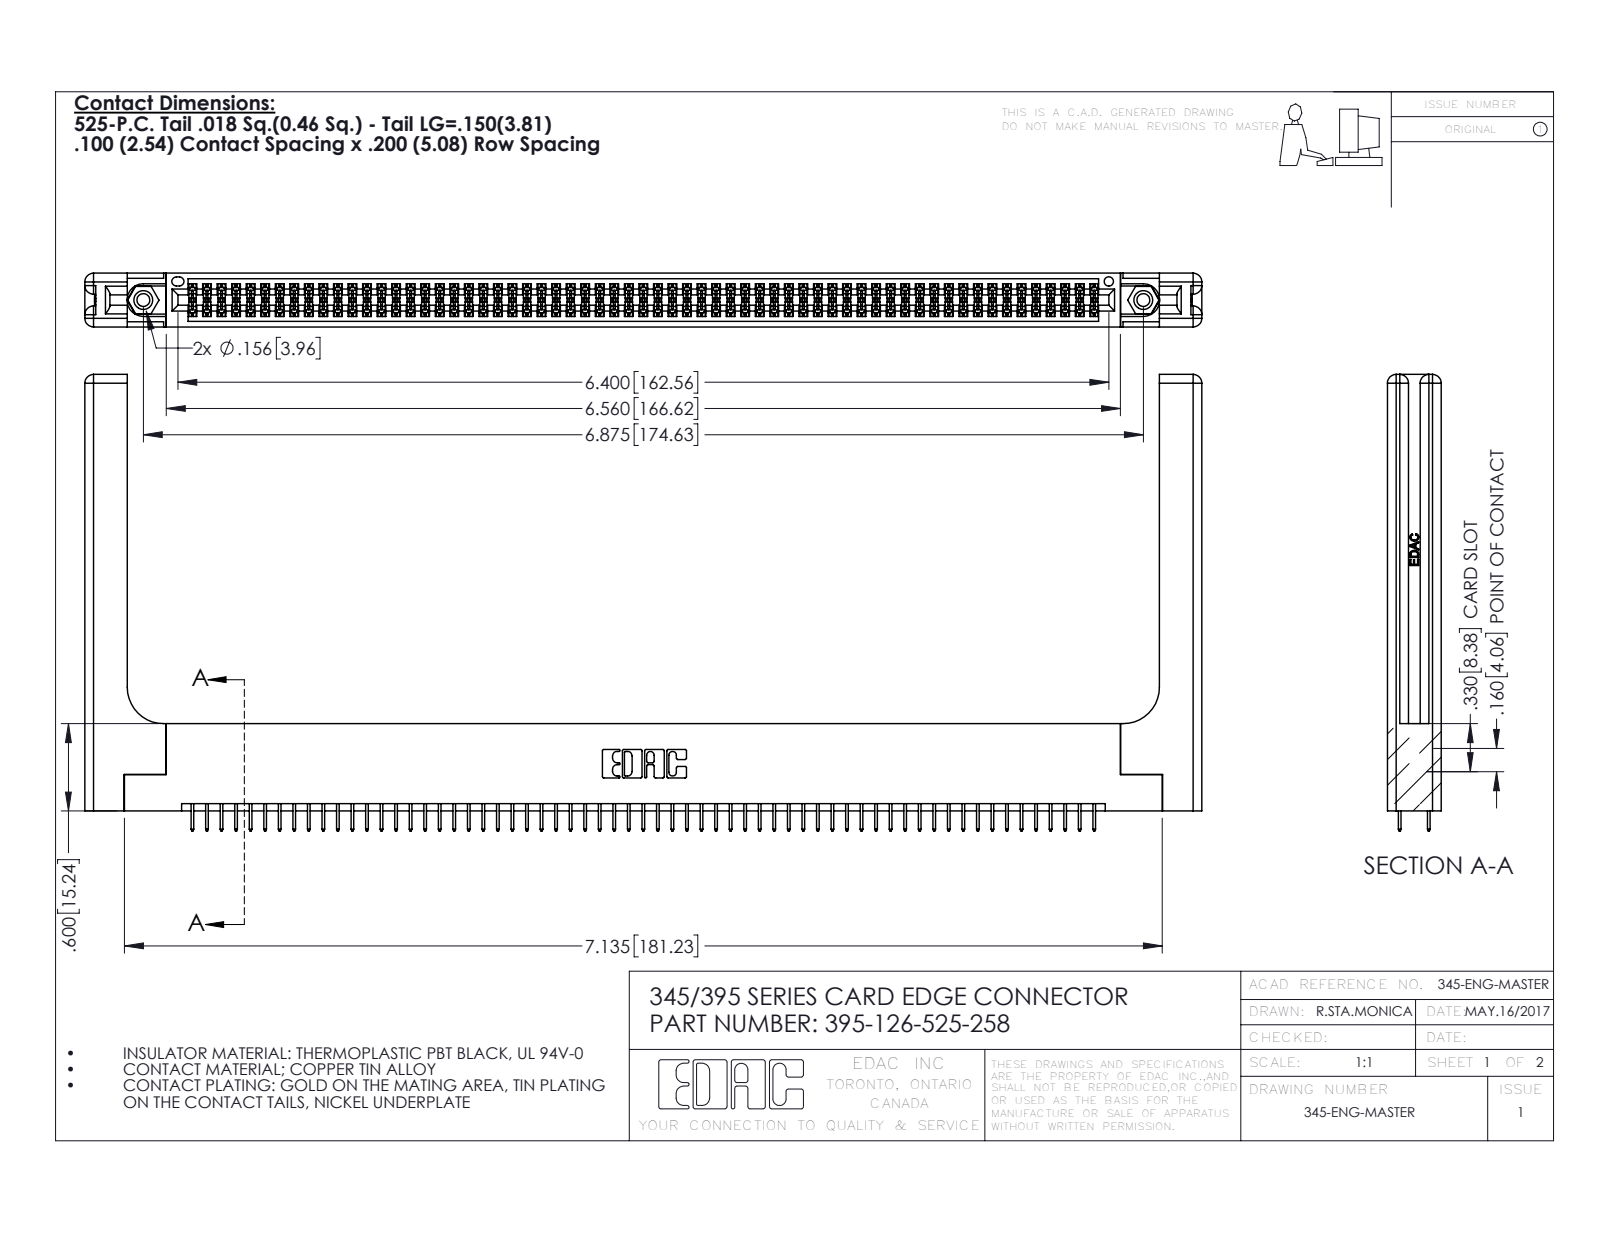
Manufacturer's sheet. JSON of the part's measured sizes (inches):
{"part_name": "345 Part_Flush Mounting Lugs - 0.156 Dia-TH; 345-292-001_345-293-125; 345-220-058_345-220-058; 345-250-001_345-250-001-102 (+1 more)", "step_written_by": "SolidWorks 2020 (CONFIG_CONTROL_DESIGN)", "units": "inches", "bodies": {"solids": 131, "faces": 7186, "planar": 5142, "cylindrical": 1984, "other": 60}, "overall_size": [7.679, 3.137, 0.37], "volume_in3": 1.673, "surface_area_in2": 50.89, "round_holes": [[0.089, 2], [0.125, 2], [0.156, 2], [0.064, 1]], "round_bosses_or_shafts": [[0.155, 2]], "partial_cylinders_radius": [[0.006, 189], [0.01, 22], [0.06, 16], [0.007, 6], [0.031, 6], [0.026, 3], [0.014, 2], [0.019, 2]], "face_to_face_distances": [0.072, 0.298, 0.37, 0.2, 0.098, 0.272, 0.025, 0.225, 0.15, 0.148], "hole_center_spacings": [0.27, 6.639, 6.875]}
